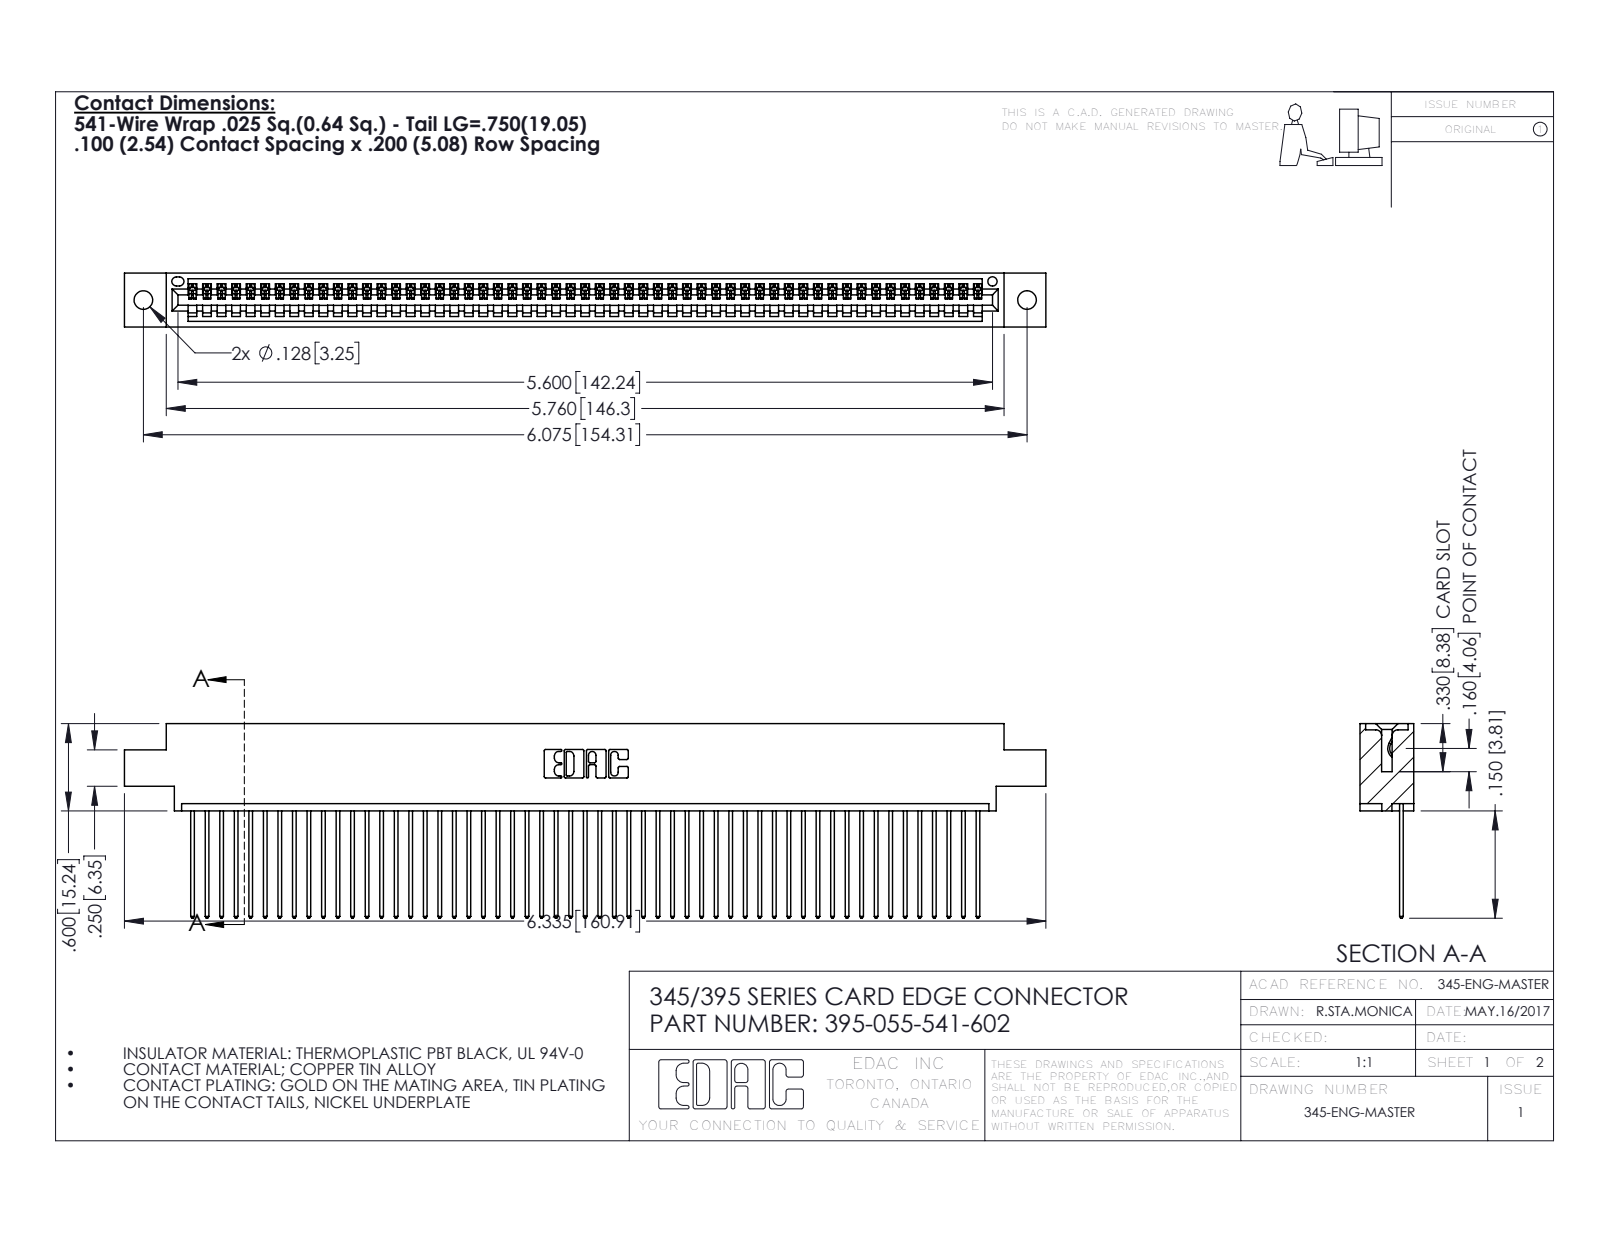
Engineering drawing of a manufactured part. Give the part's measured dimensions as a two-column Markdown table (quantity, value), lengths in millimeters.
| quantity | value |
| --- | --- |
| part name | 345 Part_0.170 Offset - 0.128 Dia; 395-055-541-602; 345-292-001_345-293-141 |
| STEP written by | SolidWorks 2016 (CONFIG_CONTROL_DESIGN) |
| units | millimeters |
| bodies | 56 solids, 3320 faces (2284 planar, 1036 cylindrical, 0 other) |
| overall size | 160.9 × 34 × 9.4 |
| volume | 15 400 mm³ |
| surface area | 21 590 mm² |
| round holes (diameter × count) | 3.3 × 2, 1.6 × 1 |
| partial cylindrical surfaces (radius × count) | 0.2 × 110, 0.3 × 110, 0.3 × 22, 0.2 × 6, 0.8 × 6, 0.7 × 3, 0.8 × 2, 1 × 2 |
| main face-to-face distances | 1.8, 7.6, 2.5, 6.9, 0.6, 9.4, 5.1, 5.7, 4.4, 3.8 |
| hole center spacings | 6.9, 148.3, 154.3 |
